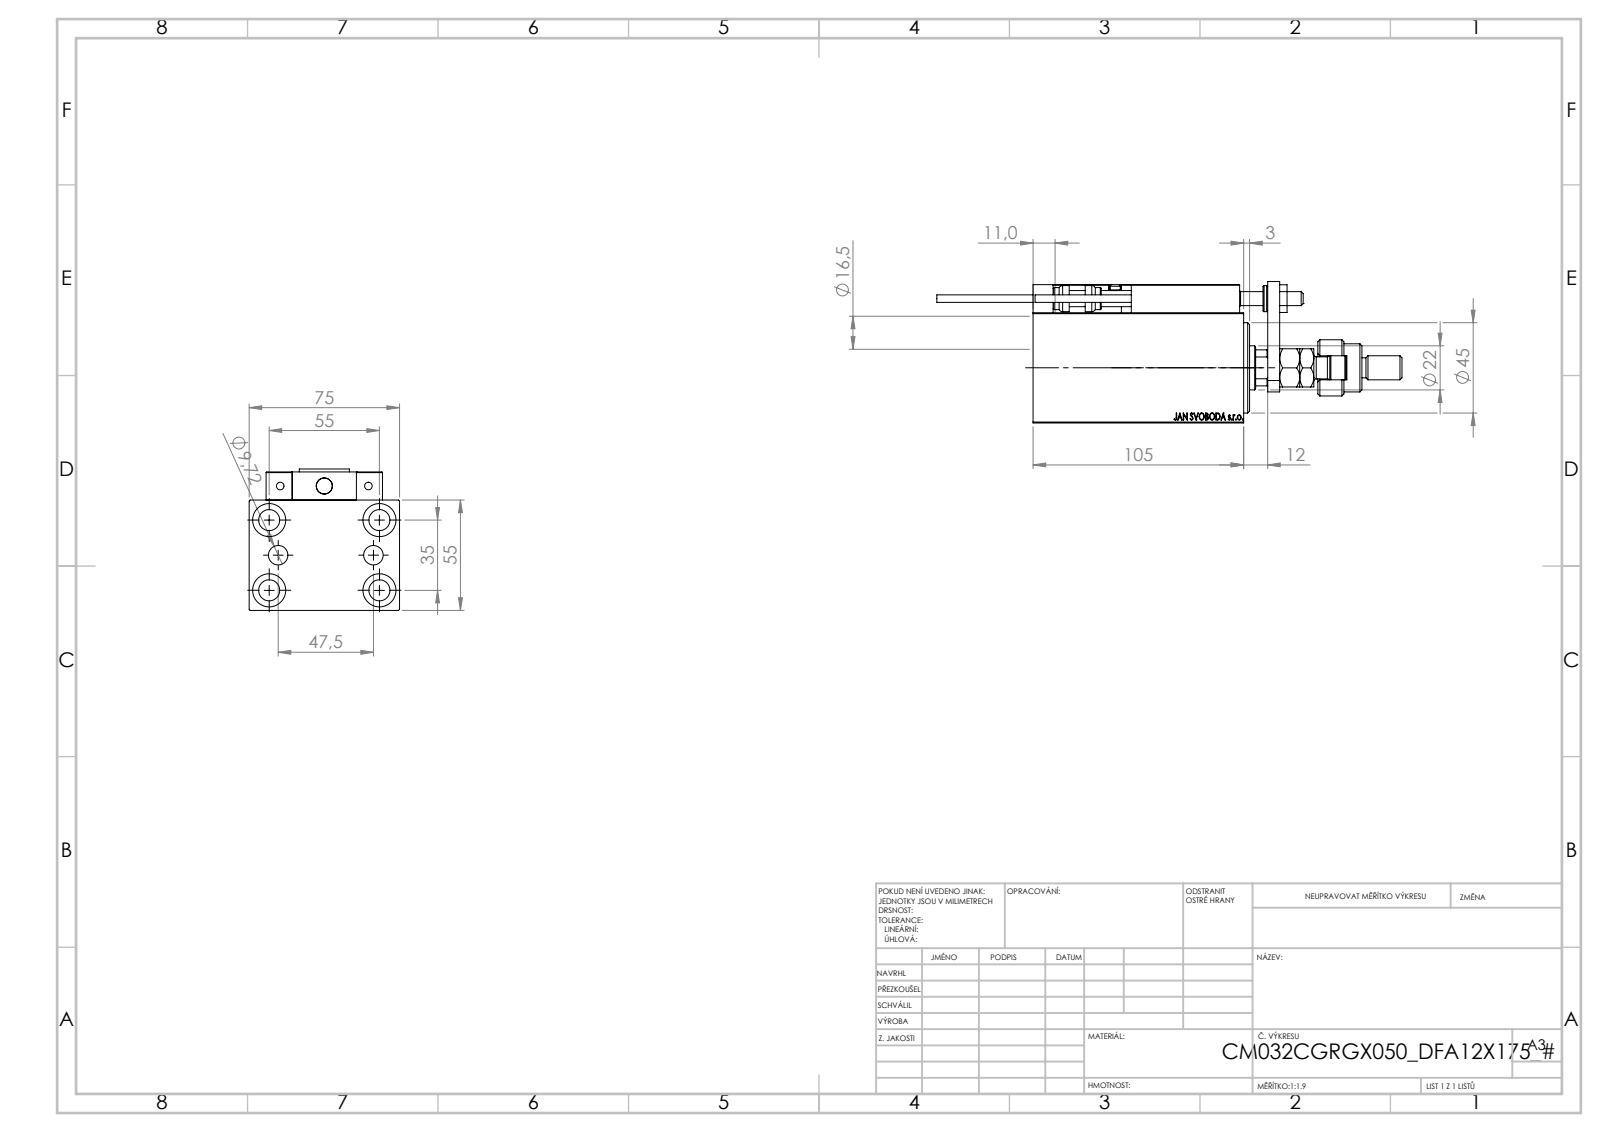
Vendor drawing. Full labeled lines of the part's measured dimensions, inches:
Part name (STEP PRODUCT): MAGNET; ZARAZKA; ALLEN BOLT D8; X_Y_DFA (+7 more)
STEP written by: SolidWorks 2019 (CONFIG_CONTROL_DESIGN)
Units: inches
Bodies: 25 solids, 1363 faces (588 planar, 197 cylindrical, 578 other)
Overall size (bounding box): 9.134 × 2.953 × 2.776
Volume: 26.44 in³ · Surface area: 174.7 in²
Round holes (diameter × count): ⌀0.157 ×6, ⌀0.315 ×5, ⌀0.413 ×5, ⌀0.65 ×5, ⌀0.126 ×4, ⌀0.197 ×2, ⌀0.383 ×2, ⌀0.276 ×1, ⌀0.866 ×1, ⌀1.004 ×1, ⌀1.26 ×1, ⌀1.339 ×1
Round bosses / shafts (diameter × count): ⌀0.433 ×2, ⌀0.197 ×2, ⌀0.15 ×2, ⌀1.102 ×1, ⌀0.945 ×1, ⌀0.709 ×1, ⌀0.512 ×1, ⌀0.472 ×1
Partial cylindrical surfaces — rounded edges, fillets, slot ends (radius × count): R0.012 ×30, R0.118 ×2, R0.384 ×1, R0.413 ×1
Main face-to-face distances: 2.165, 2.953, 0.551, 0.394, 0.709, 0.984, 2.717, 0.236, 0.197, 0.472
Hole centre spacings: 0.705, 1.283, 2.132, 0.448, 0.787, 0.935, 1.165, 1.169
